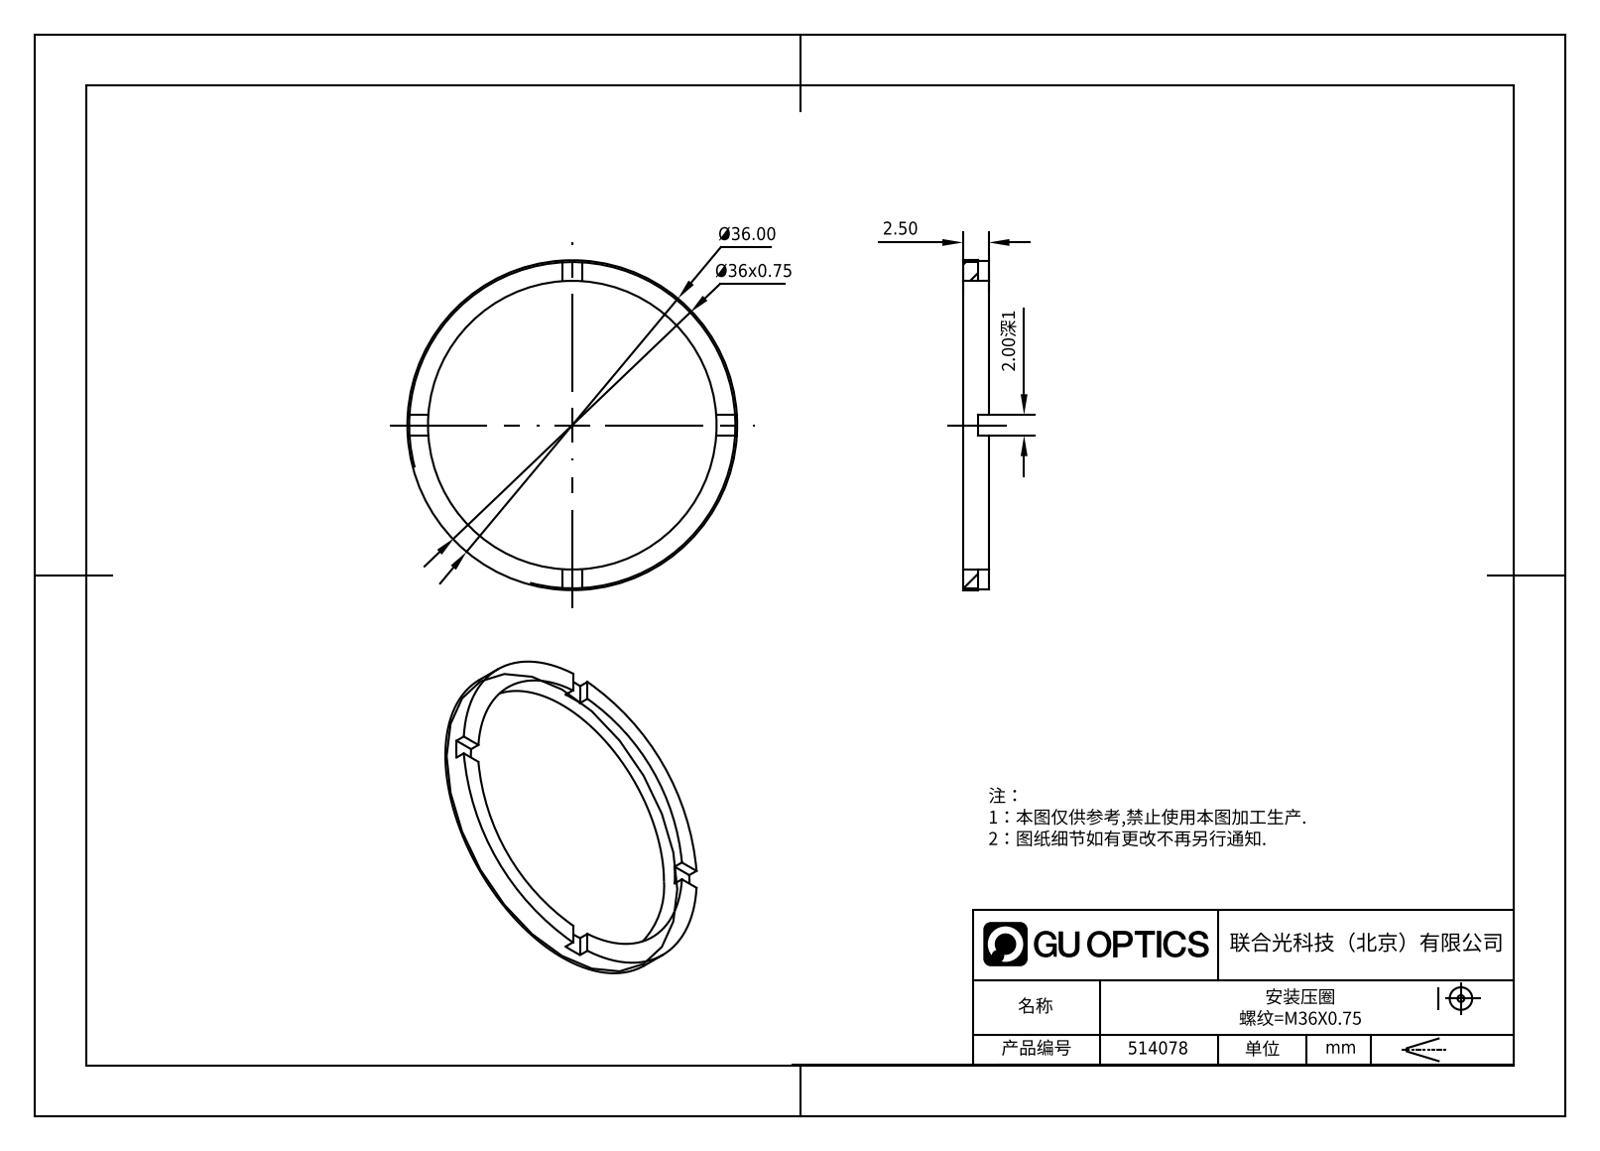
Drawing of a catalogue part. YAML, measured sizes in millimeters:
part_name: "514078"
step_written_by: "SolidWorks 2020 (CONFIG_CONTROL_DESIGN)"
units: millimeters
bodies: {solids: 1, faces: 21, planar: 17, cylindrical: 4, other: 0}
overall_size: [36, 36, 2.5]
volume: 518
surface_area: 961
round_holes:
  - {diameter: 32, count: 1}
round_bosses_or_shafts:
  - {diameter: 36, count: 1}
face_to_face_distances: [2.5, 1.5, 1, 2]
